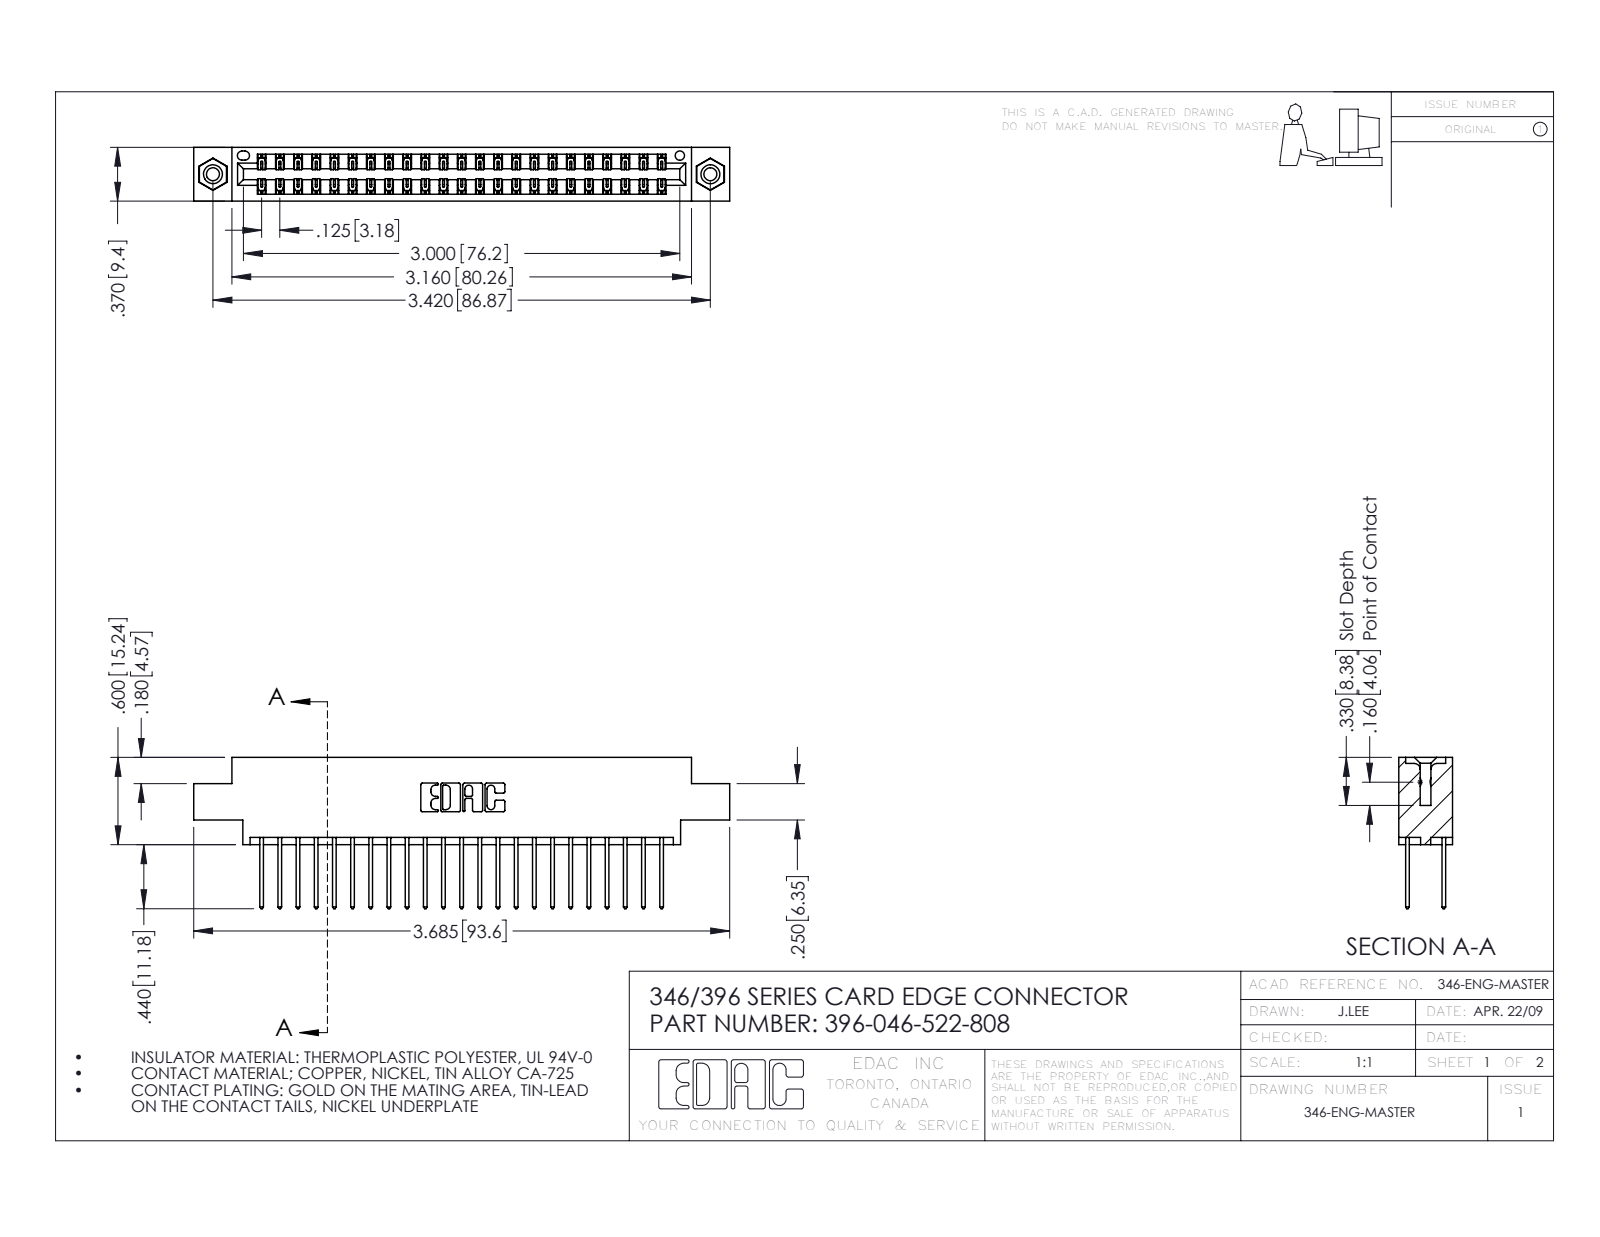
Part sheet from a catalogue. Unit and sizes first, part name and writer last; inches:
Units: inches
Overall size (bounding box): 3.685 × 1.04 × 0.37
Round holes (diameter × count): ⌀0.089 ×2, ⌀0.125 ×2, ⌀0.156 ×2, ⌀0.064 ×1
Round bosses / shafts (diameter × count): ⌀0.155 ×2
Partial cylindrical surfaces — rounded edges, fillets, slot ends (radius × count): R0.006 ×69, R0.01 ×46, R0.01 ×22, R0.007 ×6, R0.031 ×6, R0.026 ×3, R0.014 ×2, R0.022 ×2
Main face-to-face distances: 0.048, 0.322, 0.25, 0.37, 0.072, 0.298, 0.025, 0.275, 0.222, 0.148
Hole centre spacings: 0.246, 3.212, 3.42
Volume: 0.545 in³ · Surface area: 19.73 in²
Bodies: 49 solids, 2578 faces (1722 planar, 840 cylindrical, 16 other)
Part name (STEP PRODUCT): 345-250-001_345-250-003-102; 345-292-001_345-293-122; 396-046-522-808; 346 Part_0.170 Offset - 0.156 Dia-TI
STEP written by: SolidWorks 2016 (CONFIG_CONTROL_DESIGN)
